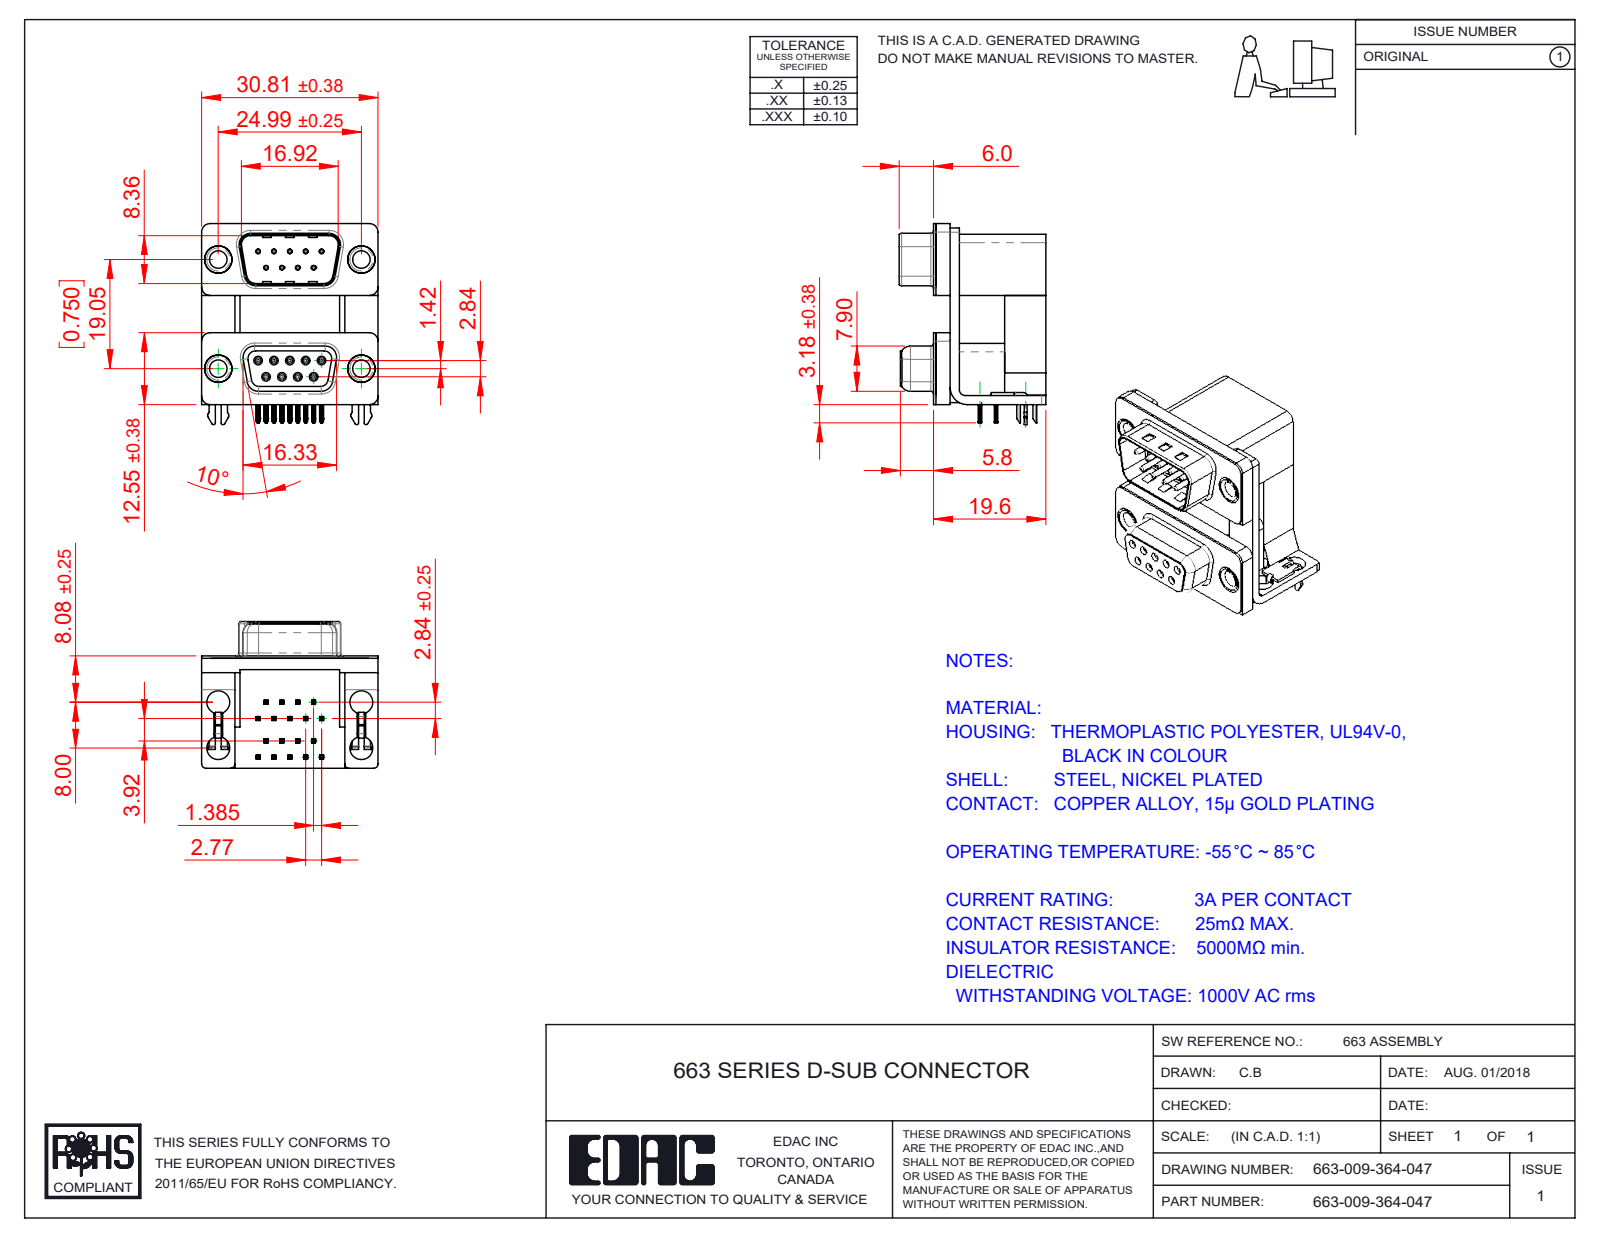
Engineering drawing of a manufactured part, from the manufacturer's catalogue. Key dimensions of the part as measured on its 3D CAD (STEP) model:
Part name (STEP PRODUCT): 663 Housing Lower_09 Contacts; 663-009-364-047; 663 Contact Top Upper_M; 663 Contact Top Lower (+8 more)
STEP written by: SolidWorks 2020 (CONFIG_CONTROL_DESIGN)
Units: millimetres
Bodies: 31 solids, 2553 faces (1341 planar, 689 cylindrical, 523 other)
Overall size (bounding box): 35.1 × 30.81 × 25.6
Volume: 10 779 mm³ · Surface area: 12 602 mm²
Round holes (diameter × count): ⌀0.8 ×18, ⌀0.35 ×9, ⌀0.9 ×9, ⌀4 ×8, ⌀3.05 ×4, ⌀3.5 ×4, ⌀4.8 ×4, ⌀5 ×4
Round bosses / shafts (diameter × count): ⌀1.2 ×9, ⌀0.75 ×9, ⌀4.9 ×4, ⌀4.75 ×4, ⌀3.85 ×4
Partial cylindrical surfaces — rounded edges, fillets, slot ends (radius × count): R0.1 ×73, R0.25 ×42, R0.15 ×36, R0.12 ×18, R0.35 ×18, R0.5 ×16, R1.5 ×15, R0.75 ×10
Main face-to-face distances: 0.4, 2.5, 16.7, 19.2, 7.2, 9.5, 12, 1.6, 19.6, 12.4
Hole centre spacings: 3.16, 2.77, 19.25, 19.05, 5.54, 19.84, 16.27, 21.93
